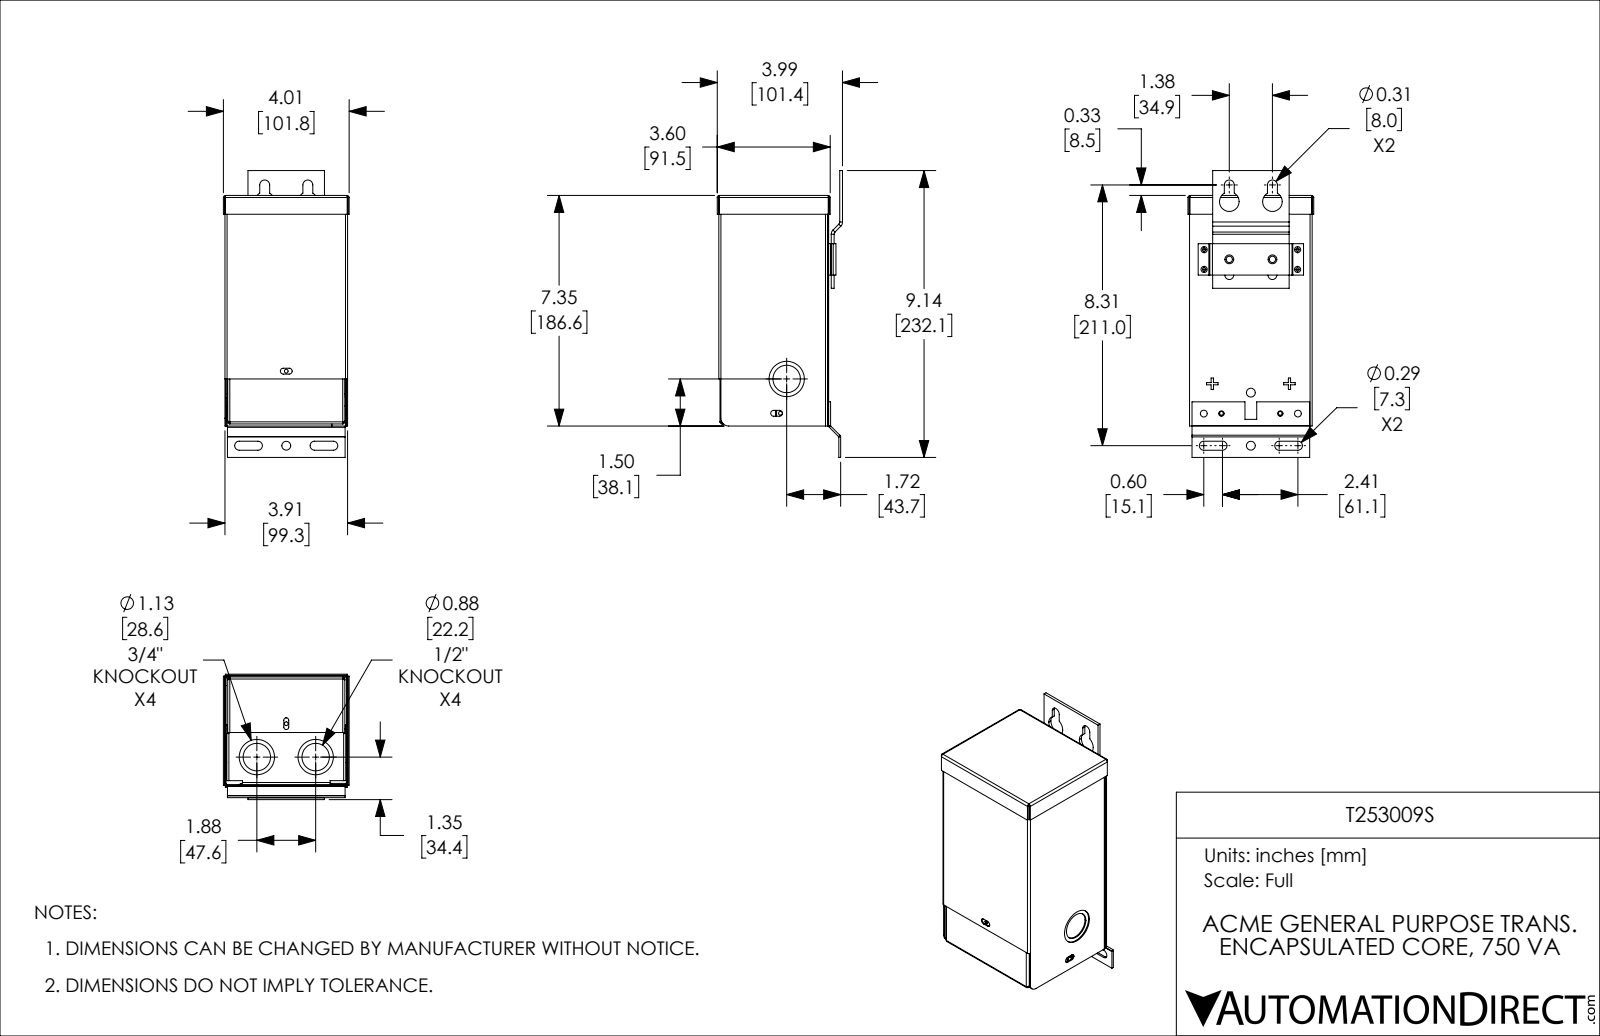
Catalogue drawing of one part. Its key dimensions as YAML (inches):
part_name: "T253009S"
step_written_by: "SolidWorks 2021 (CONFIG_CONTROL_DESIGN)"
units: inches
bodies: {solids: 7, faces: 528, planar: 326, cylindrical: 154, other: 48}
overall_size: [9.137, 4.008, 3.993]
volume: 6.9
surface_area: 352.5
round_holes:
  - {diameter: 0.12, count: 5}
  - {diameter: 0.281, count: 3}
  - {diameter: 0.281, count: 3}
  - {diameter: 0.875, count: 3}
  - {diameter: 1.125, count: 3}
  - {diameter: 0.171, count: 2}
  - {diameter: 0.187, count: 2}
  - {diameter: 0.201, count: 2}
  - {diameter: 0.218, count: 2}
  - {diameter: 0.625, count: 2}
  - {diameter: 1.125, count: 1}
round_bosses_or_shafts:
  - {diameter: 1.197, count: 3}
  - {diameter: 0.947, count: 3}
partial_cylinders:
  - {radius: 0.031, count: 16}
  - {radius: 0.067, count: 16}
  - {radius: 0.094, count: 8}
  - {radius: 0.026, count: 4}
  - {radius: 0.086, count: 4}
  - {radius: 0.144, count: 4}
  - {radius: 0.017, count: 2}
  - {radius: 0.077, count: 2}
face_to_face_distances: [0.036, 3.464, 3.874, 3.428, 3.91, 3.839, 3.5, 0.06, 7.242, 7.182]
hole_center_spacings: [1.375, 0.5, 0.502, 0.562, 0.563, 1.145, 1.151, 1.376]
